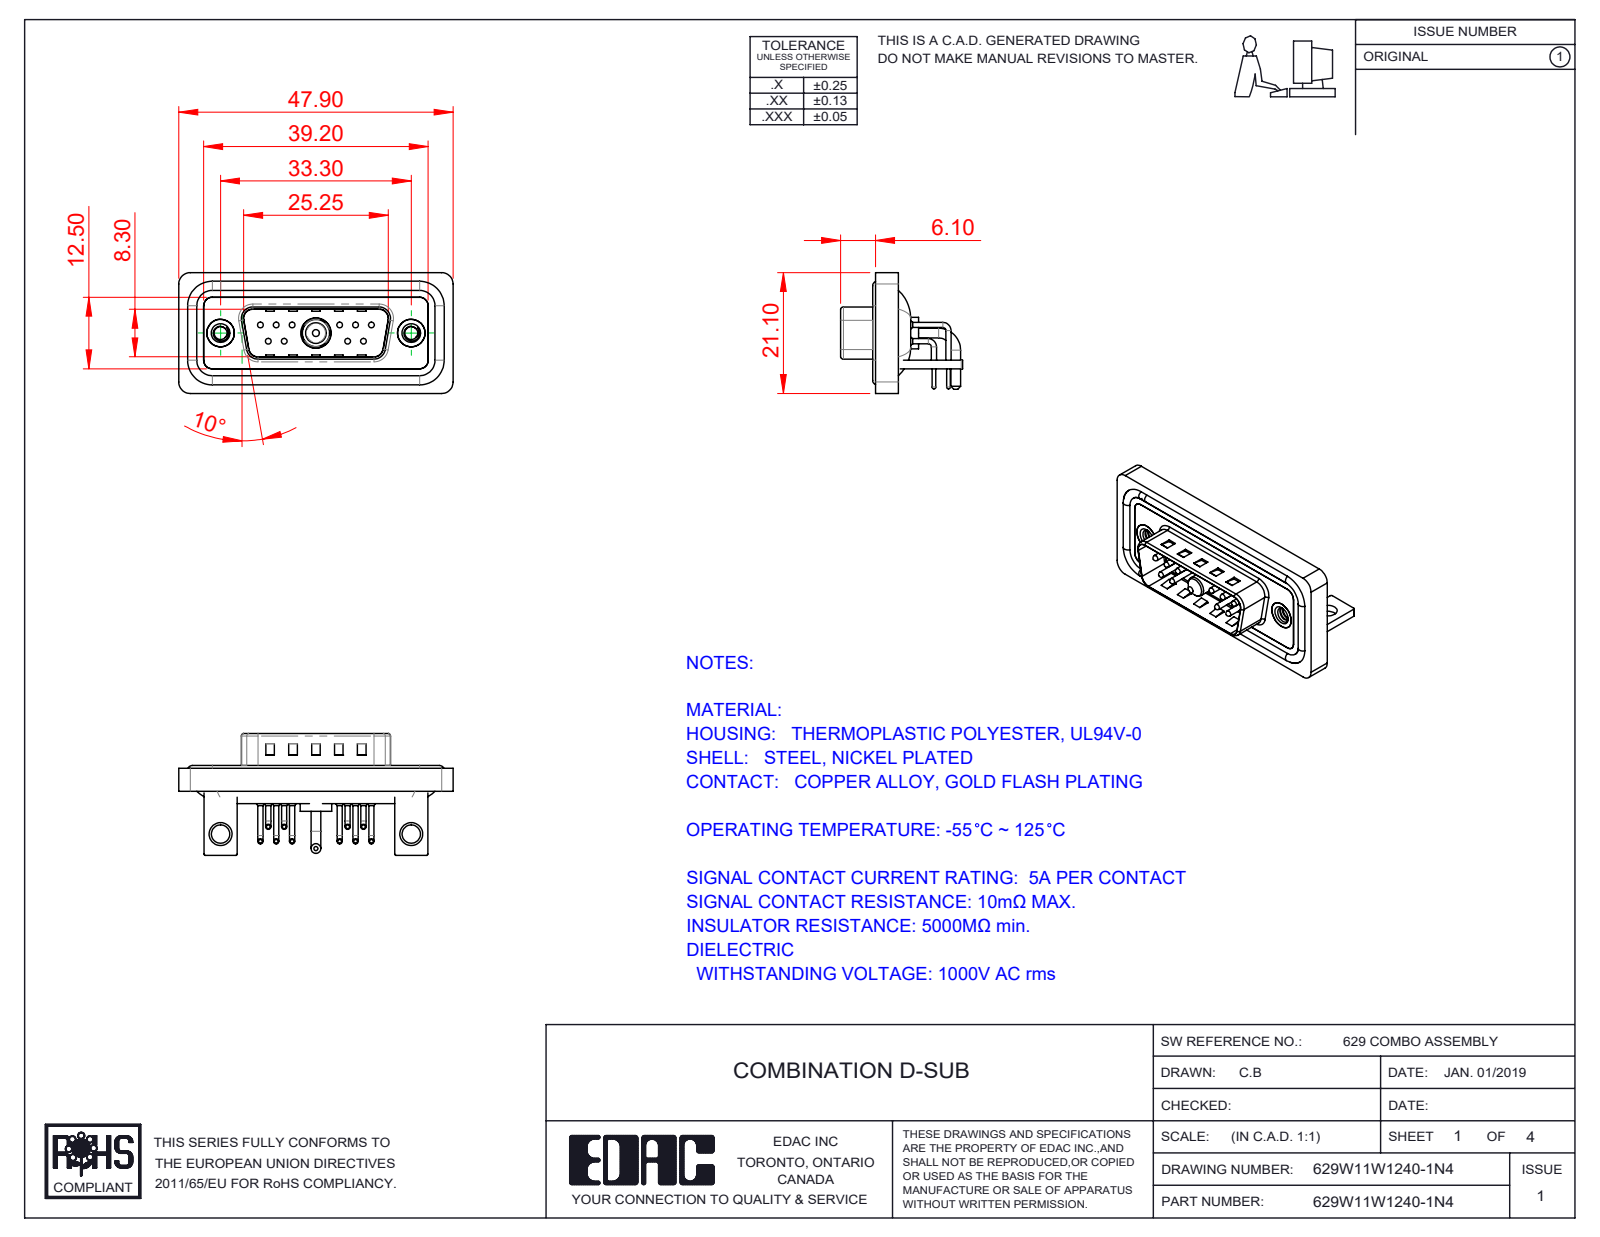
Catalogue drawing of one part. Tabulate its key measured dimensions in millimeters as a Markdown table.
| quantity | value |
| --- | --- |
| part name | 629Combo Threaded Rivet_3; 629Combo Contact Row 2; 629W11W1240-1N4; 629Combo Housing_11W1 (+6 more) |
| STEP written by | SolidWorks 2020 (CONFIG_CONTROL_DESIGN) |
| units | millimeters |
| bodies | 21 solids, 1643 faces (856 planar, 587 cylindrical, 200 other) |
| overall size | 47.9 × 21.3 × 21.1 |
| volume | 5 809 mm³ |
| surface area | 9 816 mm² |
| round holes (diameter × count) | 0.75 × 10, 1.6 × 10, 2 × 10, 2.26 × 2, 3.2 × 2, 4 × 2, 4.8 × 2, 5 × 2, 4.85 × 1, 5.3 × 1 |
| round bosses / shafts (diameter × count) | 0.9 × 20, 1.5 × 10, 1 × 10, 0.65 × 10, 1.6 × 4, 4.9 × 2, 1.7 × 2, 5.5 × 1 |
| partial cylindrical surfaces (radius × count) | 2 × 21, 1.5 × 18, 0.25 × 16, 1.01 × 10, 0.5 × 9, 1.6 × 8, 1 × 7, 0.6 × 4 |
| main face-to-face distances | 0.4, 0.8, 1.5, 2.9, 2.1, 1.1, 1.6, 1.2, 3.7, 4.1 |
| hole center spacings | 3.16, 2.77, 13.85, 11.08, 16.62, 5.03, 5.04, 5.54 |
